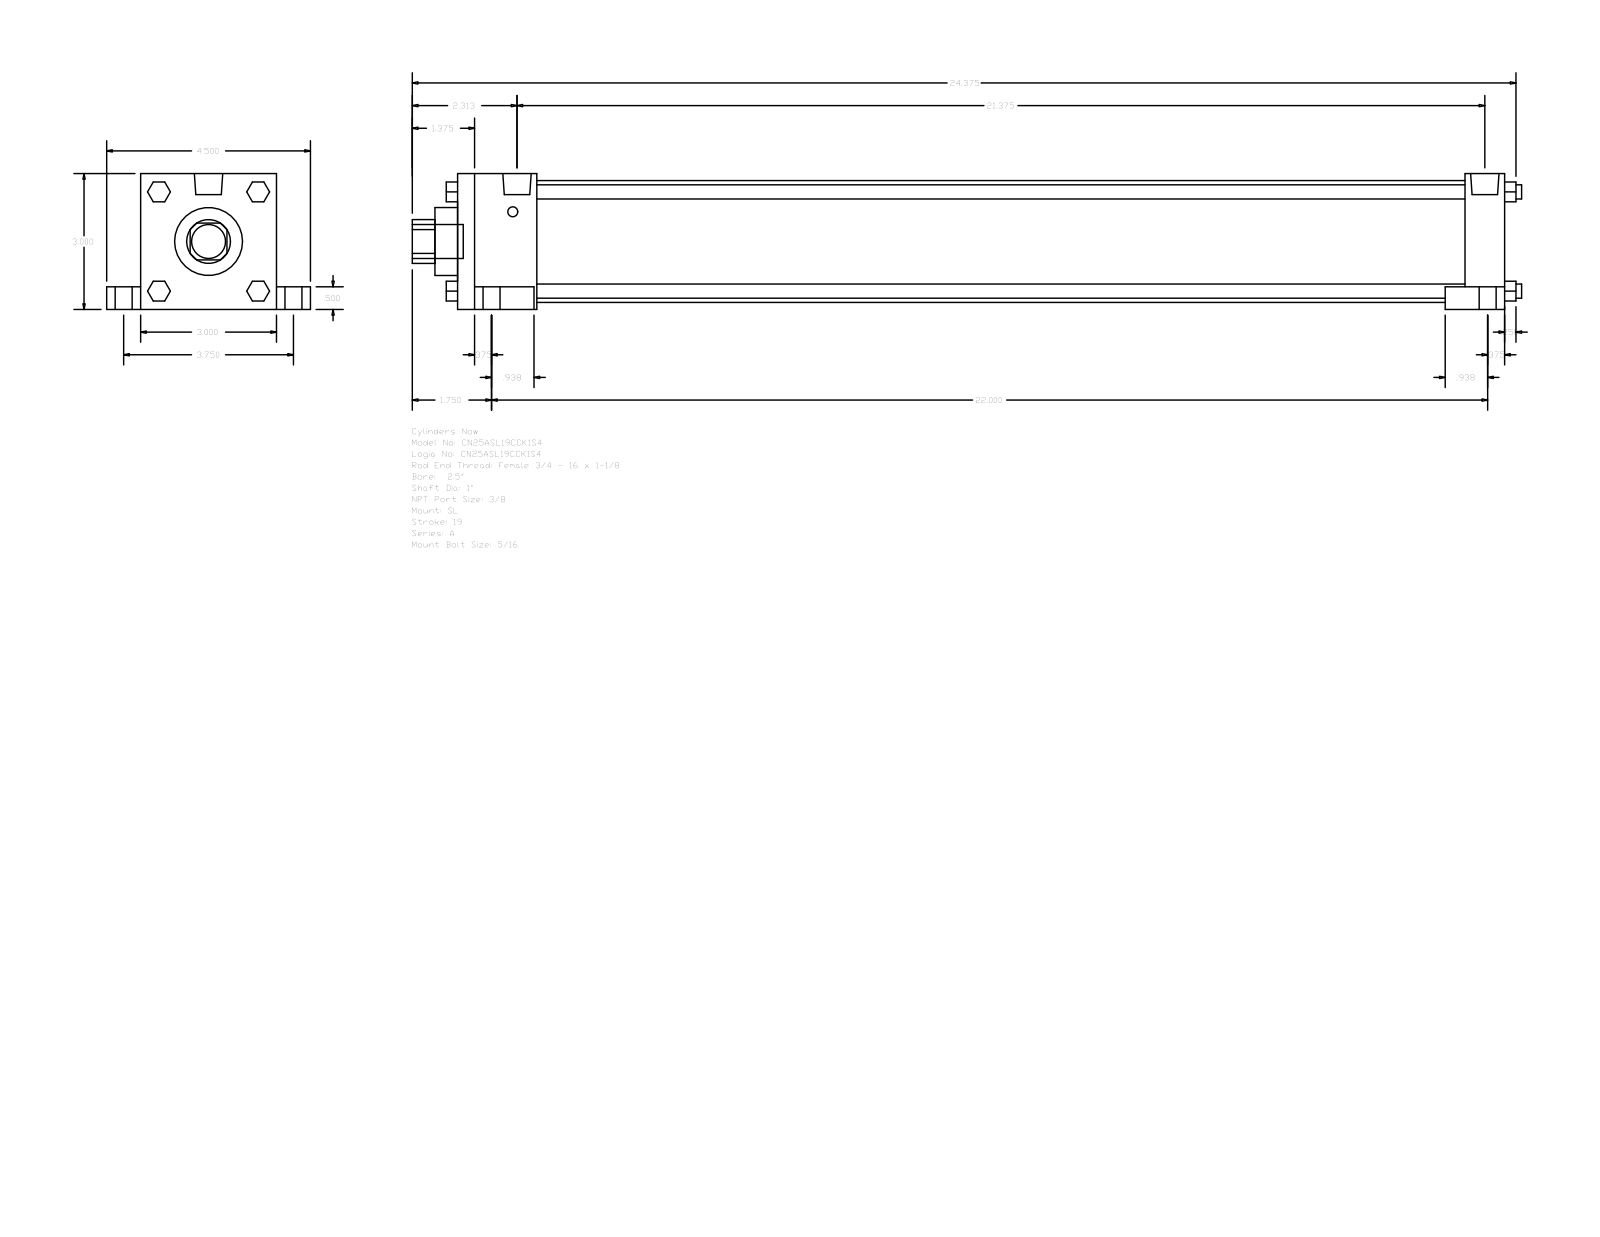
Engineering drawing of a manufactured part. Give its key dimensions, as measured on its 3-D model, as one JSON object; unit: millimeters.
{"part_name": "A_SL__0250_1", "step_written_by": "GSSL Pune (CONFIG_CONTROL_DESIGN)", "units": "millimeters", "bodies": {"solids": 0, "faces": 148, "planar": 112, "cylindrical": 36, "other": 0}, "overall_size": [622.3, 114.3, 76.2], "round_holes": [[25.4, 1], [38.1, 1], [68.33, 1]], "round_bosses_or_shafts": [[15.88, 4], [9.53, 4], [7.94, 4], [5.56, 4], [15.93, 2], [19.05, 1]], "partial_cylinders_radius": [[12.29, 1]], "face_to_face_distances": [76.2, 587.37, 12.7, 22.22, 44.45, 542.92, 565.15, 520.7, 19.05, 63.5]}
